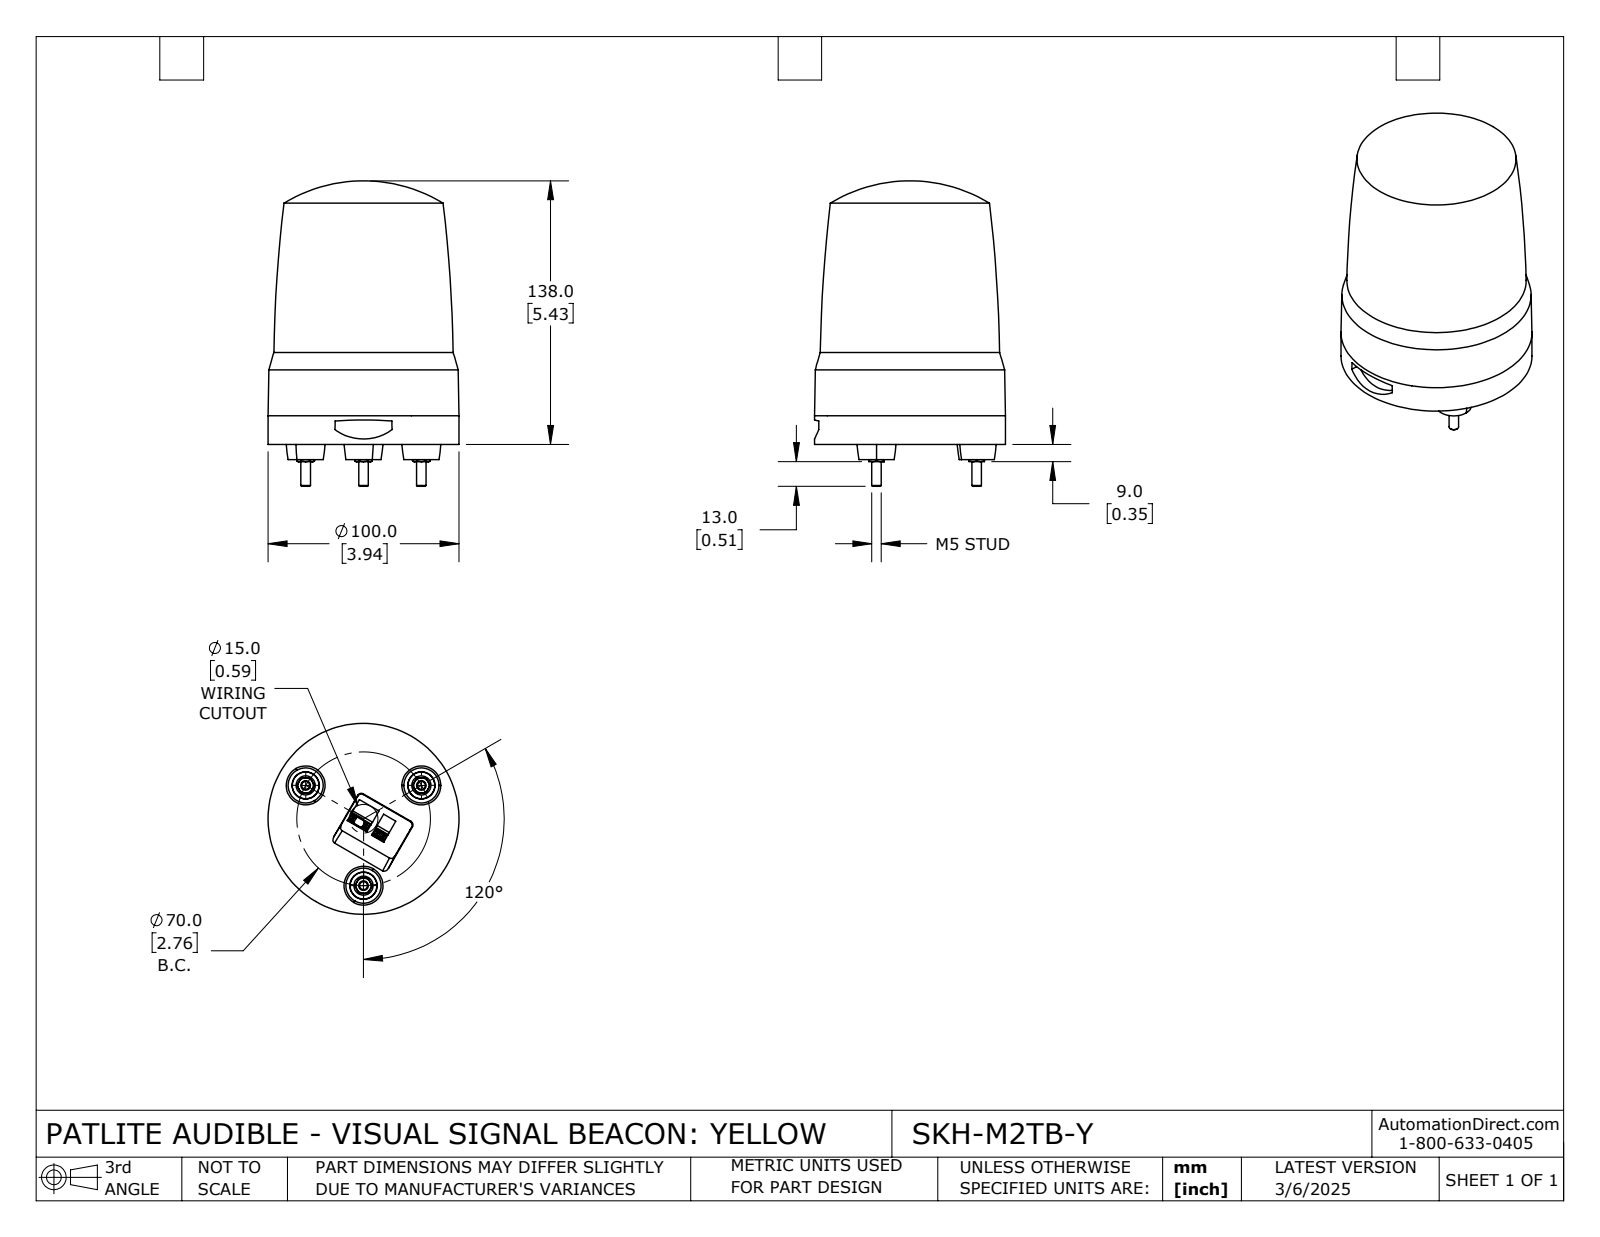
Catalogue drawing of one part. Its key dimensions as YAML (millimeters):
part_name: "SKH-M2TB-Y"
step_written_by: "SolidWorks 2024 (CONFIG_CONTROL_DESIGN)"
units: millimeters
bodies: {solids: 1, faces: 270, planar: 146, cylindrical: 25, other: 99}
overall_size: [160, 100, 100]
volume: 895705
surface_area: 57629
round_bosses_or_shafts:
  - {diameter: 10, count: 3}
  - {diameter: 5, count: 3}
  - {diameter: 100, count: 1}
partial_cylinders:
  - {radius: 2, count: 4}
  - {radius: 0.3, count: 2}
  - {radius: 5.05, count: 2}
  - {radius: 45, count: 1}
  - {radius: 80.12, count: 1}
face_to_face_distances: [18.85, 8, 22, 26.85, 3, 3.8, 4.2, 23.05, 5.95, 14.82]
